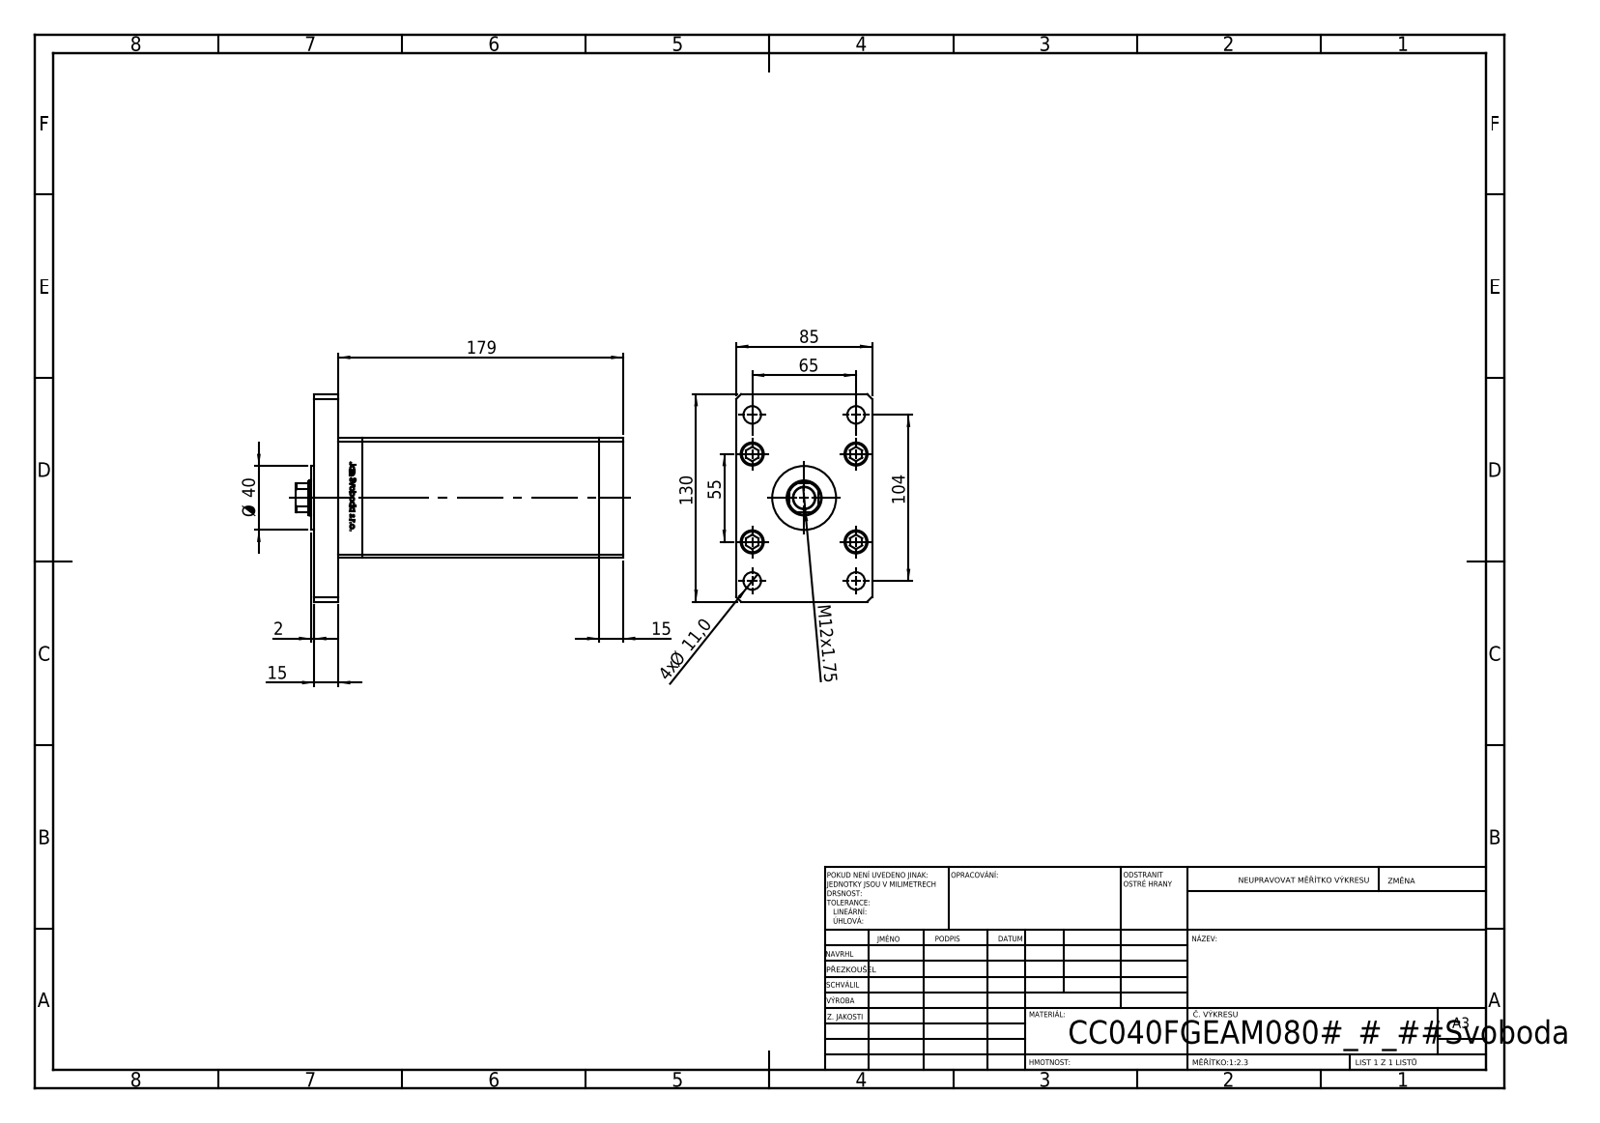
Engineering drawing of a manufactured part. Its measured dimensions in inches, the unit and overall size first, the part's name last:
Units: inches
Overall size (bounding box): 8.071 × 5.118 × 3.346
Round holes (diameter × count): ⌀0.433 ×9, ⌀0.61 ×5, ⌀0.394 ×4, ⌀0.571 ×4, ⌀0.079 ×2, ⌀0.518 ×2, ⌀0.531 ×1, ⌀0.866 ×1, ⌀0.925 ×1
Round bosses / shafts (diameter × count): ⌀0.315 ×9, ⌀0.571 ×5, ⌀1.575 ×1
Partial cylindrical surfaces — rounded edges, fillets, slot ends (radius × count): R0.037 ×2, R0.413 ×1
Main face-to-face distances: 0.591, 3.346, 6.437, 7.028, 2.953, 1.181, 5.846, 7.618, 0.413, 1.083
Hole centre spacings: 1.102, 0.965, 1.676, 2.414, 2.559, 2.735, 3.13, 4.043
Volume: 71.09 in³ · Surface area: 308.3 in²
Bodies: 19 solids, 1310 faces (517 planar, 187 cylindrical, 606 other)
Part name (STEP PRODUCT): V220C BACK_F; V220C_FRONT_F; V220C_F; ALLEN BOLT (+2 more)
STEP written by: SolidWorks 2019 (CONFIG_CONTROL_DESIGN)
